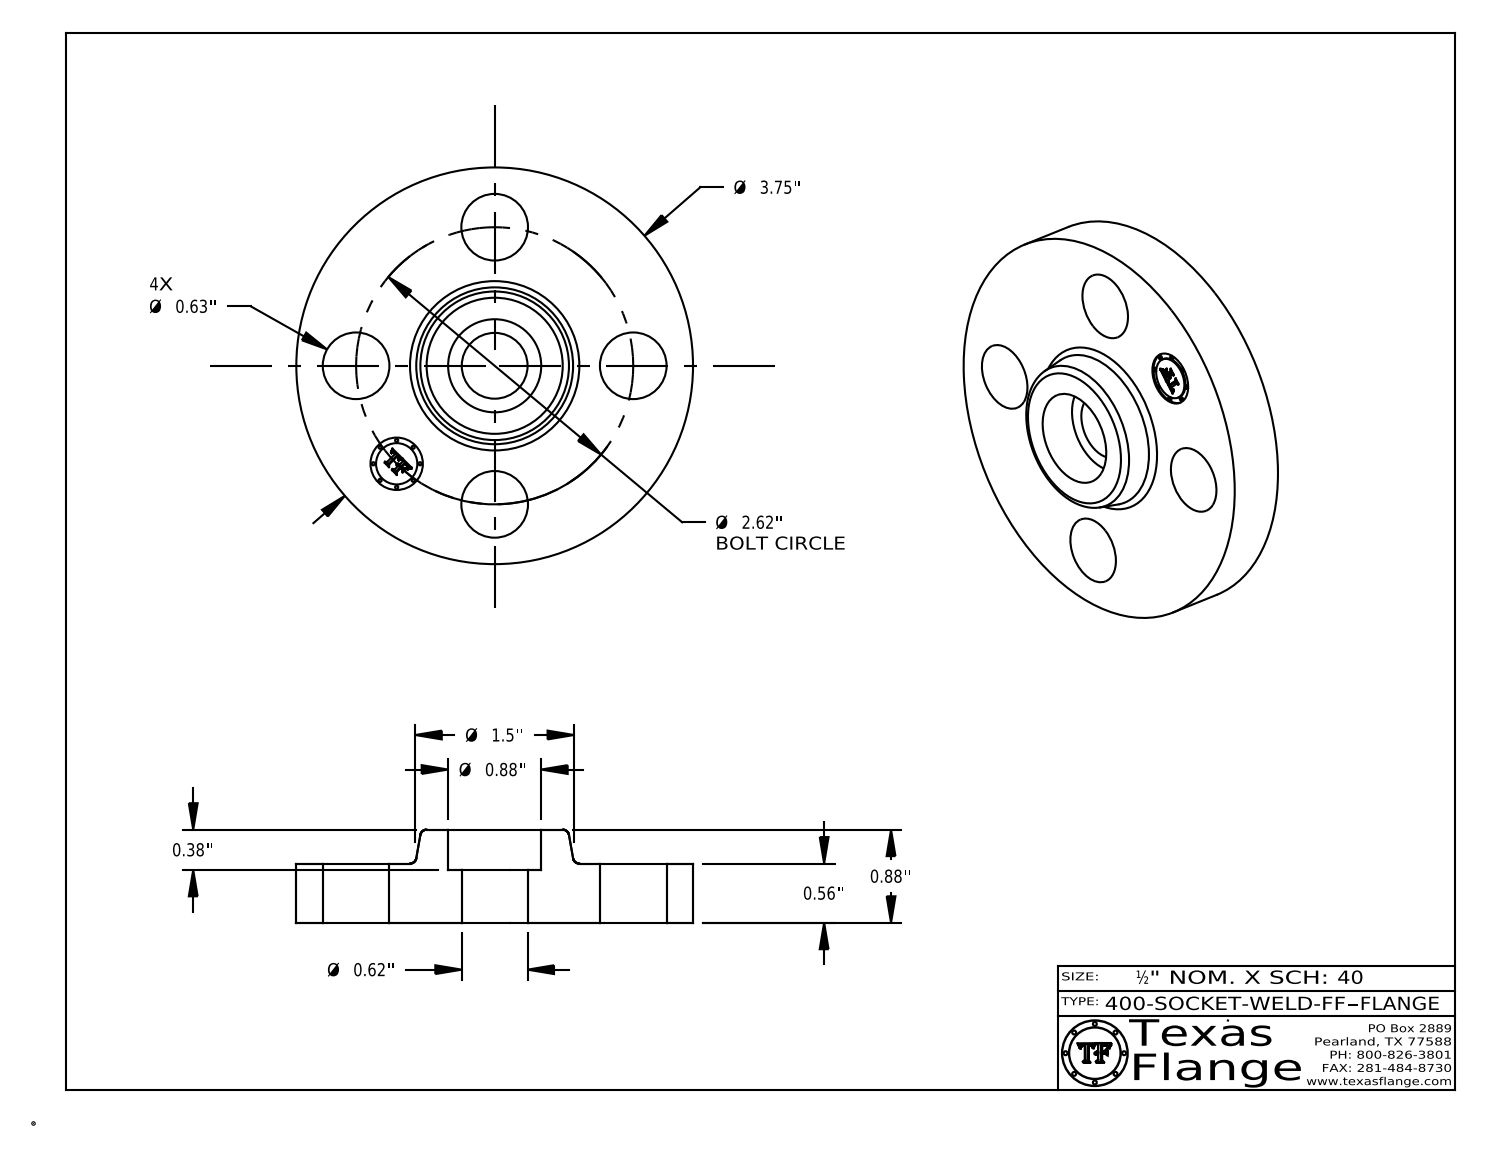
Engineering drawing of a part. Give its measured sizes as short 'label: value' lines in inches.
name: 400-SOCKET-WELD-FF
written by: CATIA V5 STEP AP214 (AUTOMOTIVE_DESIGN)
unit: in
bodies: 1 solid, 409 faces (369 planar, 34 cylindrical, 6 other)
size: 3.75 × 3.75 × 0.88
volume: 5.627 in³; area: 33.2 in²
holes: 4× ⌀0.63, 1× ⌀0.495, 1× ⌀0.622, 1× ⌀0.88
bosses: 8× ⌀0.03, 1× ⌀3.75, 1× ⌀0.39
face distances: 0.56, 0.88, 0.32, 0.5, 0.06, 0.38, 0.545, 0.045, 0.015, 0.335
hole spacings: 1.31, 1.852, 1.003, 2.42, 2.62, 1.31
